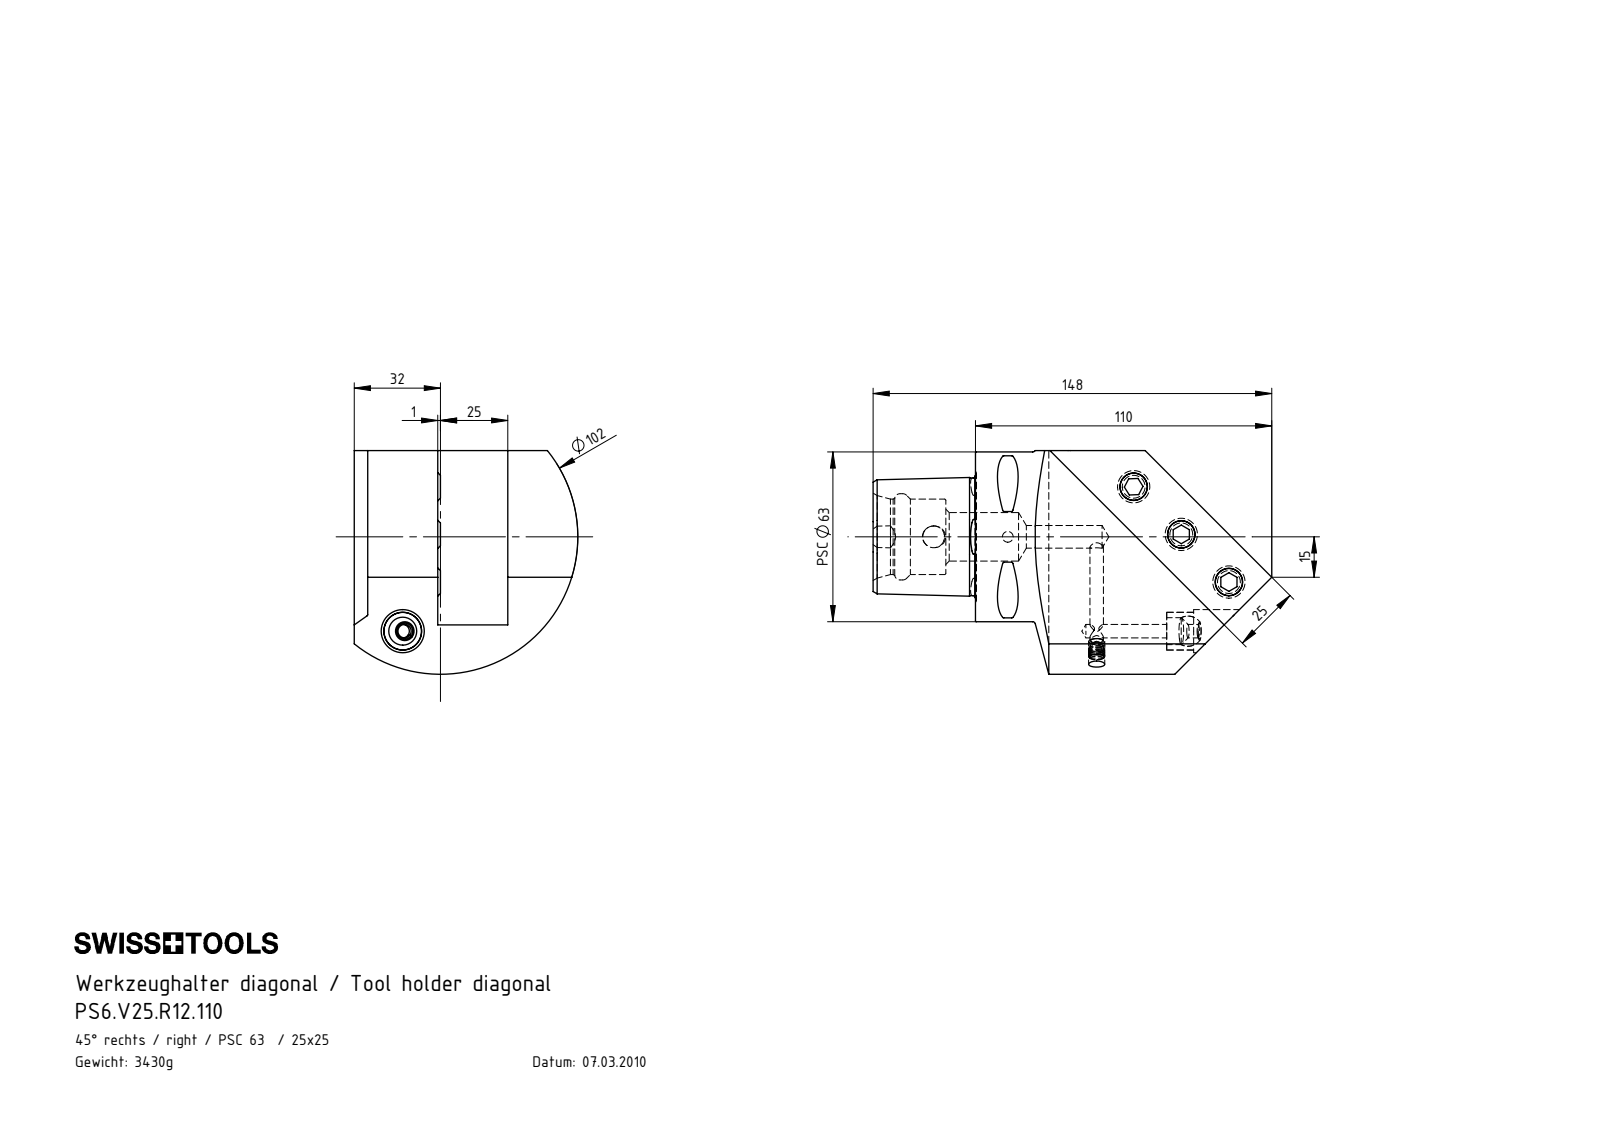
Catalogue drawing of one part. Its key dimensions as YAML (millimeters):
part_name: "KVT_MB_600_060; PS6.V25.R12.110; ISO 4026 - M12 x 25_PreviewCfg; KU1-U14.001.012 (+3 more)"
step_written_by: "SolidWorks 2017 (AUTOMOTIVE_DESIGN)"
units: millimeters
bodies: {solids: 8, faces: 254, planar: 62, cylindrical: 64, other: 128}
overall_size: [148, 83, 83]
volume: 437551
surface_area: 57455
round_holes:
  - {diameter: 5, count: 4}
  - {diameter: 10.2, count: 3}
  - {diameter: 4, count: 1}
  - {diameter: 6, count: 1}
  - {diameter: 8.1, count: 1}
  - {diameter: 8.4, count: 1}
  - {diameter: 10, count: 1}
  - {diameter: 14, count: 1}
  - {diameter: 16, count: 1}
  - {diameter: 18, count: 1}
  - {diameter: 28, count: 1}
  - {diameter: 32, count: 1}
round_bosses_or_shafts:
  - {diameter: 12, count: 3}
  - {diameter: 63, count: 1}
  - {diameter: 6, count: 1}
partial_cylinders:
  - {radius: 0.5, count: 8}
  - {radius: 6, count: 1}
  - {radius: 51, count: 1}
face_to_face_distances: [26, 25, 57, 31, 52, 5, 38, 27, 24.88, 6]
hole_center_spacings: [25, 27.5, 37.7, 50.01, 50.29, 64.42, 76.52, 83.79]
